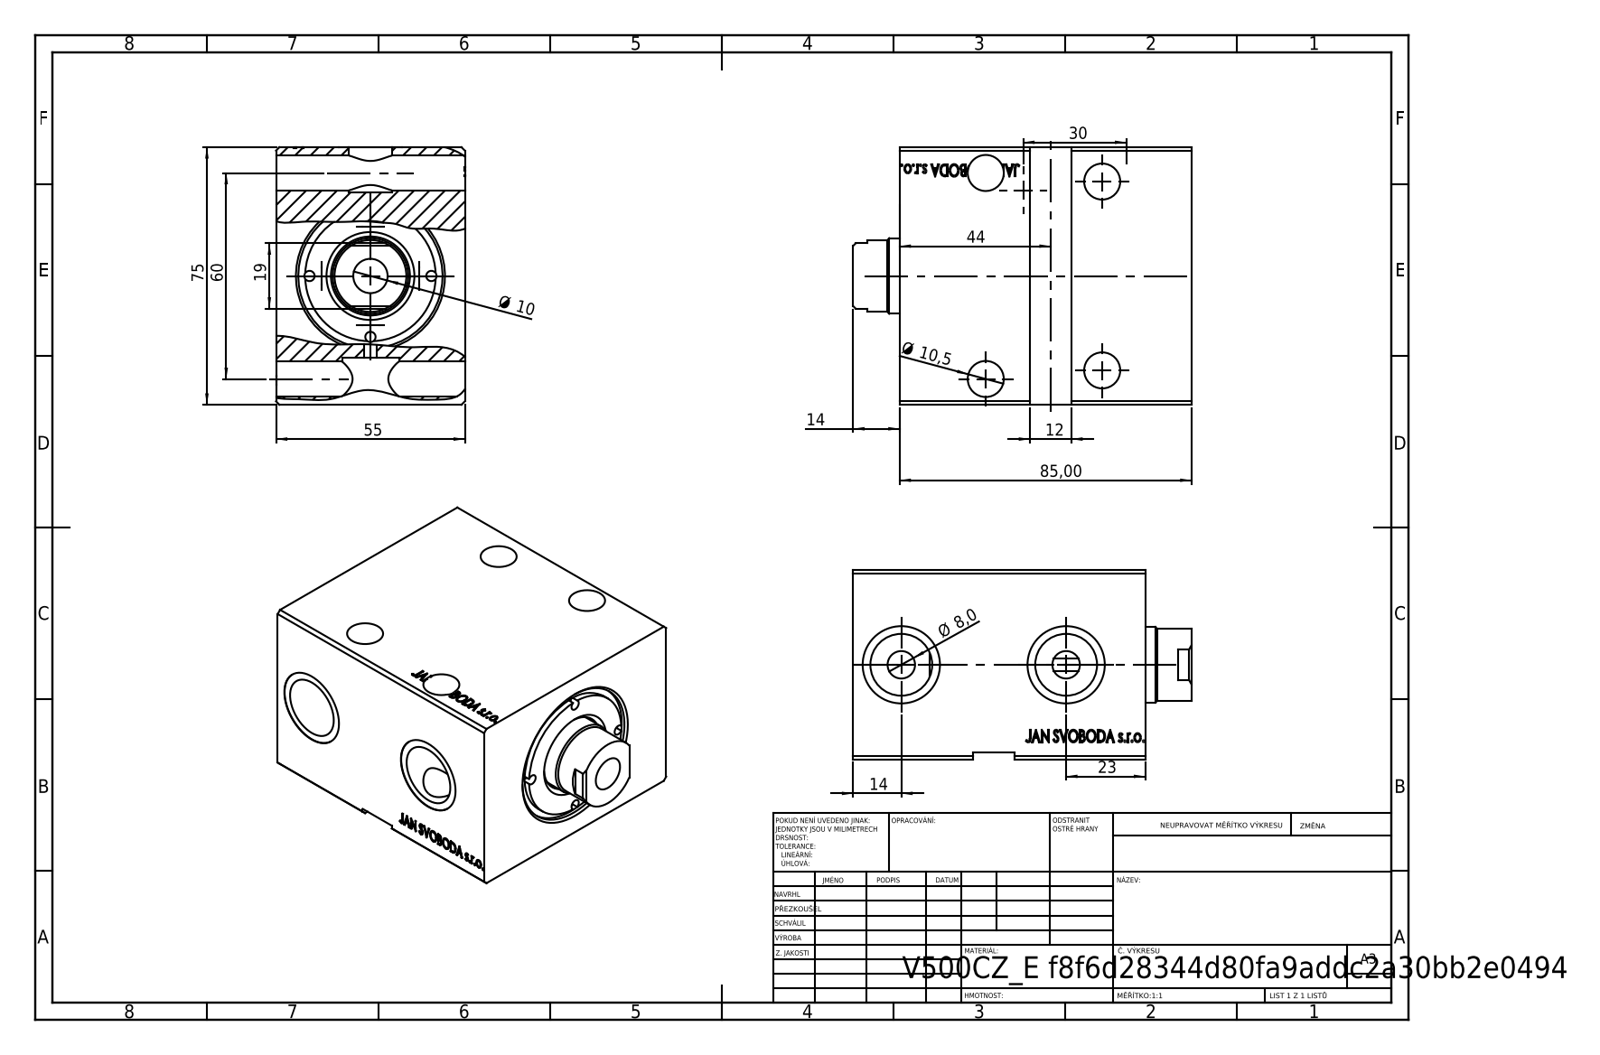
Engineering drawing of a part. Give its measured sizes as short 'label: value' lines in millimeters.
name: V500CZ_E; V500CZ_VCP_E; V500CZ_VC_vysunovaci_E
written by: SolidWorks 2019 (CONFIG_CONTROL_DESIGN)
unit: mm
bodies: 3 solids, 800 faces (381 planar, 67 cylindrical, 352 other)
size: 98.5 × 75 × 55
volume: 312 859 mm³; area: 57 055 mm²
holes: 4× ⌀3, 4× ⌀10.5, 4× ⌀18, 4× ⌀22.5, 2× ⌀5.5, 2× ⌀8, 1× ⌀10, 1× ⌀22, 1× ⌀23, 1× ⌀32, 1× ⌀36, 1× ⌀42
bosses: 1× ⌀38, 1× ⌀20.92
face distances: 55, 75, 85, 30, 84.8, 29.8, 11.8, 43.2, 73, 73.2
hole spacings: 17.75, 25.1, 34, 35.5, 66.75, 1, 3, 48
